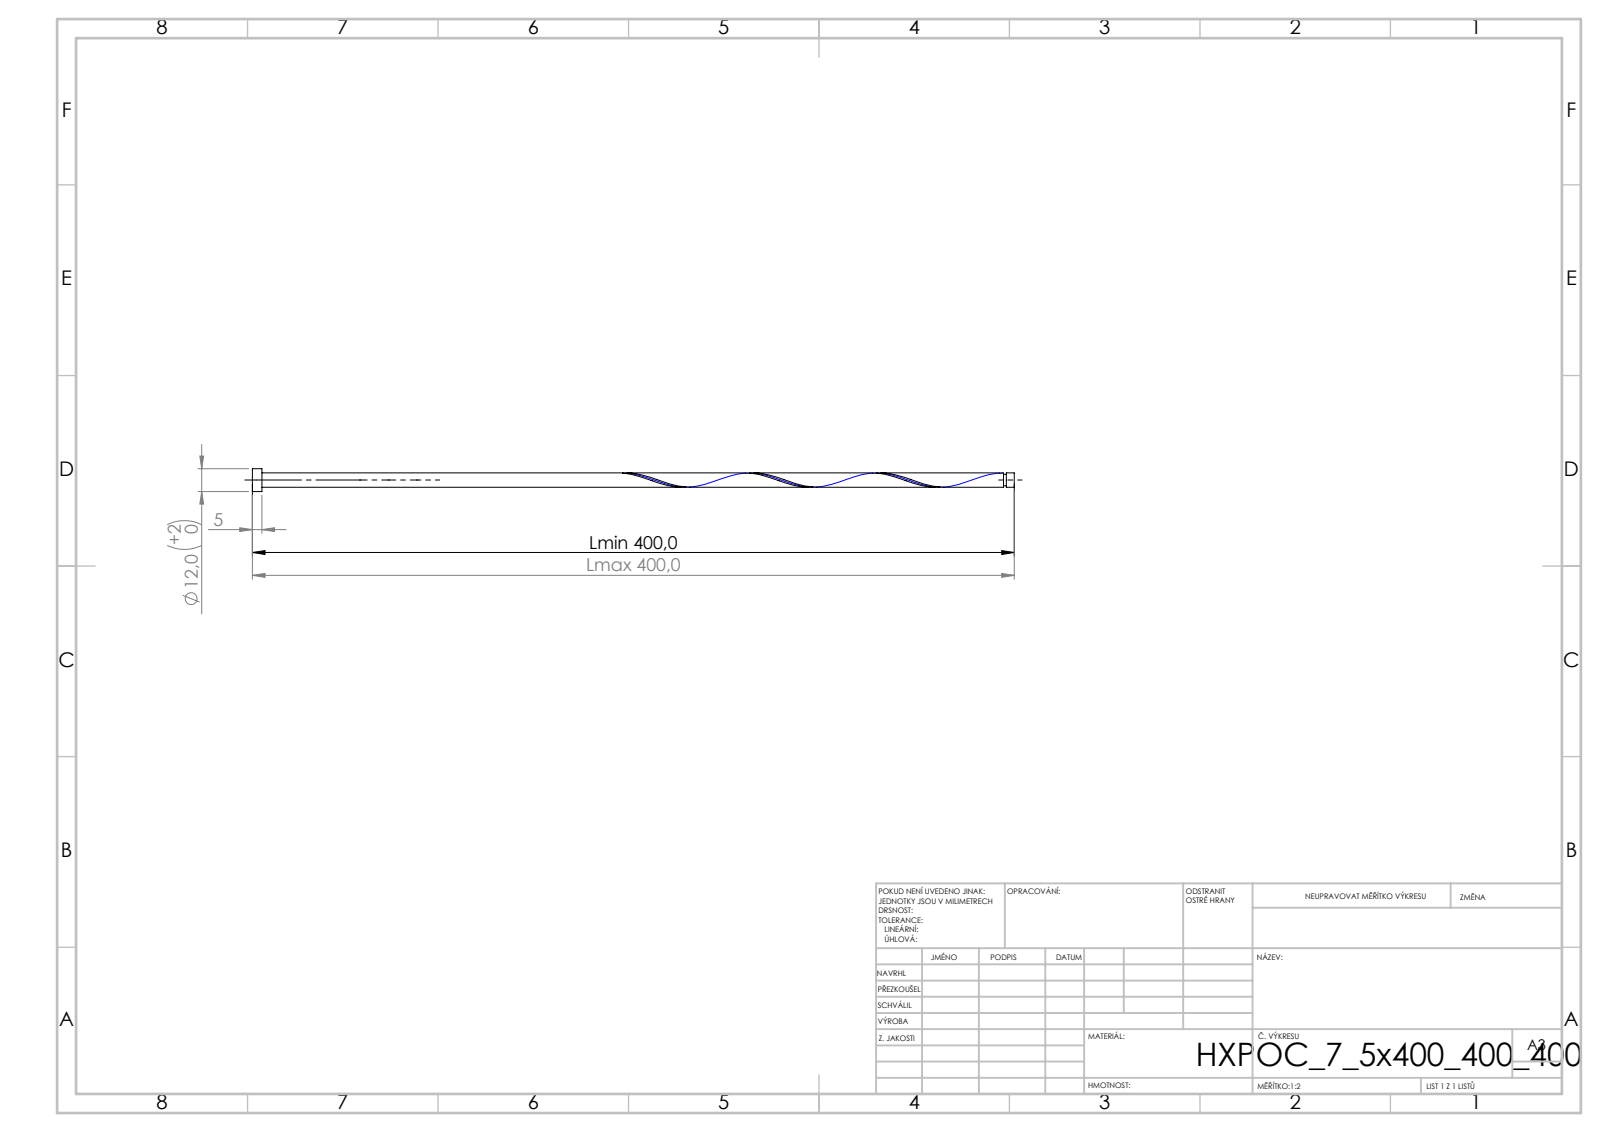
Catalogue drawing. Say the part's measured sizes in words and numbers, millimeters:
Its 3-D file was written by "SolidWorks 2019 (CONFIG_CONTROL_DESIGN)". It is 1 solid with 16 faces: 6 planar, 9 cylindrical and 1 other. Overall it measures 400 by 12 by 12 millimeters. Its volume is 21 752 cubic millimeters and its surface area 13 043 square millimeters. Round bosses or shafts: 1 of diameter 12, 1 of diameter 7.5, 1 of diameter 6. The main face-to-face distances are 5, 400, 395, 395.8, 390.8, 4.2, 394.3, 389.3, 1.5, 5.7.
